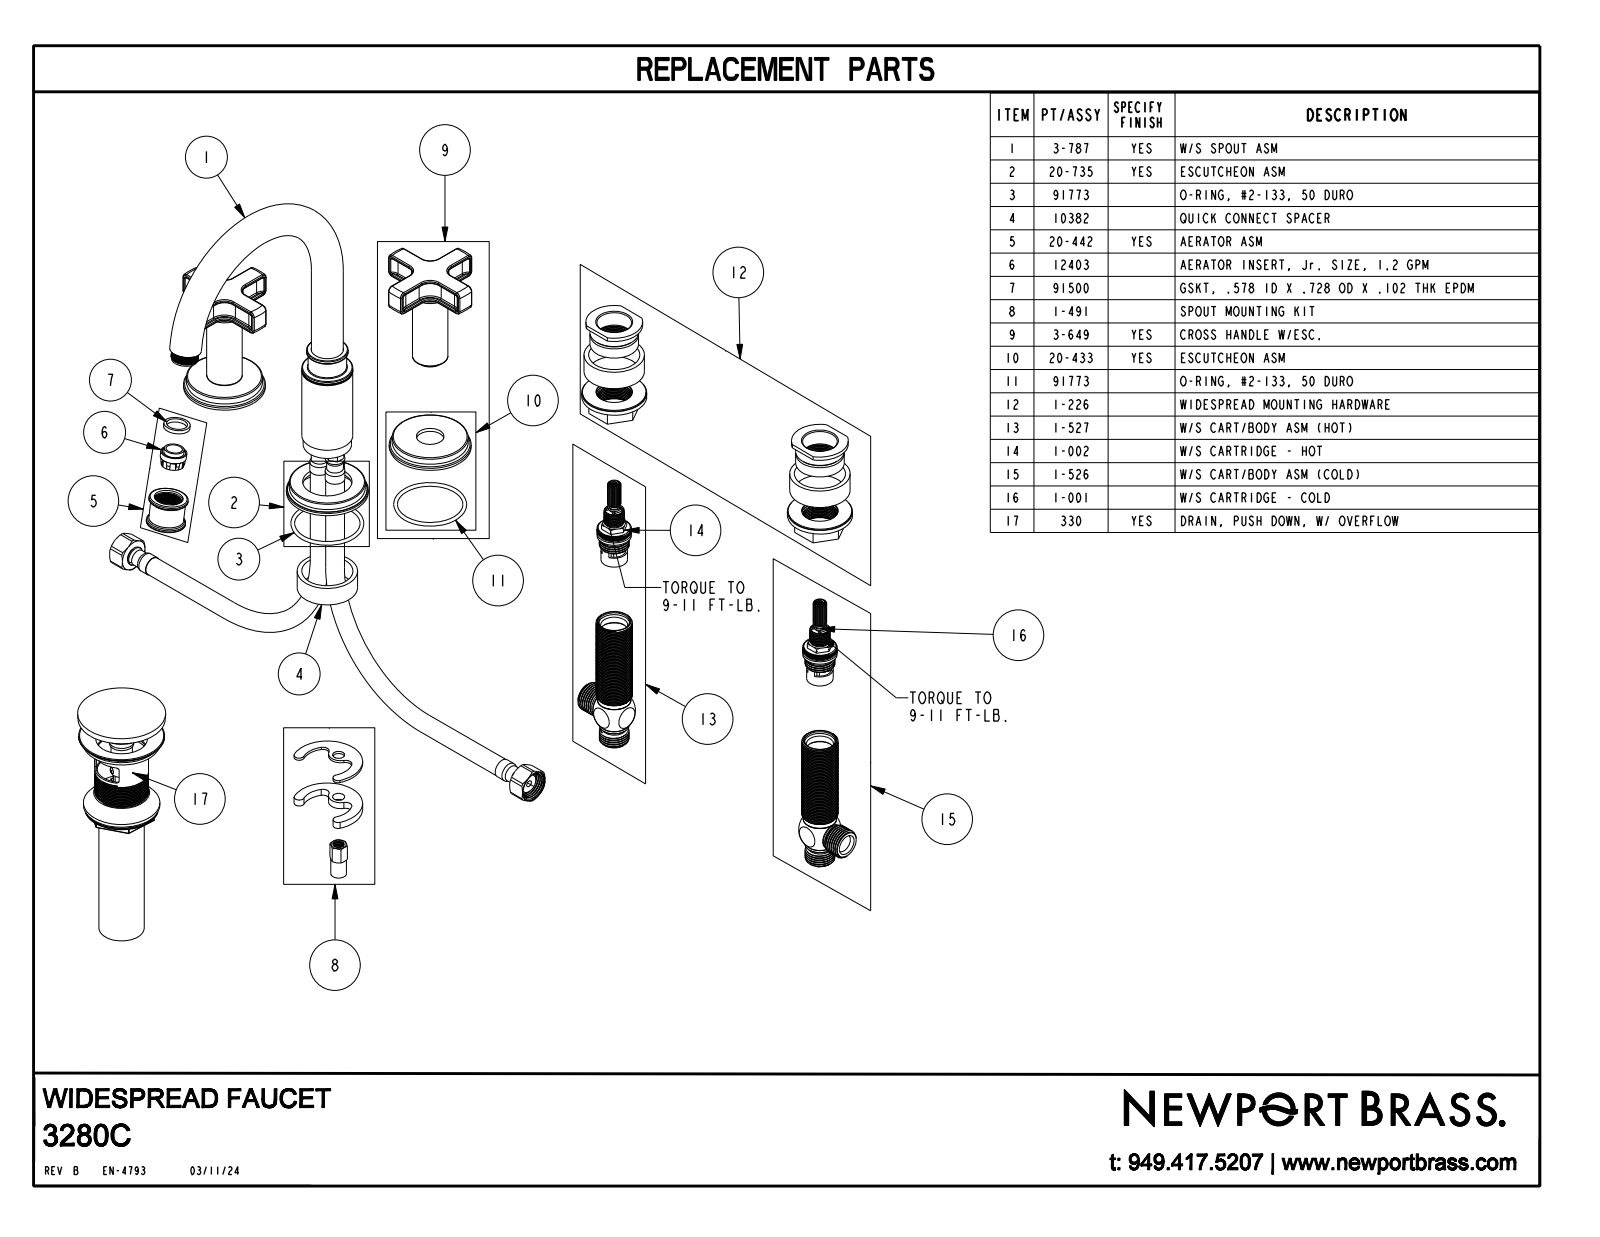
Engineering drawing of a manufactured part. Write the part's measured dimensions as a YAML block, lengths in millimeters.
part_name: "3280C"
step_written_by: "CREO PARAMETRIC BY PTC INC, 2023134 (CONFIG_CONTROL_DESIGN)"
units: millimeters
bodies: {solids: 5, faces: 748, planar: 174, cylindrical: 316, other: 258}
overall_size: [274.3, 231.2, 192]
volume: 347700
surface_area: 77870
round_holes:
  - {diameter: 2.8, count: 2}
  - {diameter: 9.1, count: 2}
  - {diameter: 10.2, count: 2}
  - {diameter: 14.2, count: 2}
  - {diameter: 17.6, count: 1}
round_bosses_or_shafts:
  - {diameter: 57.2, count: 3}
  - {diameter: 53.1, count: 3}
  - {diameter: 24.8, count: 2}
  - {diameter: 22.2, count: 2}
  - {diameter: 21.6, count: 2}
  - {diameter: 35.6, count: 1}
  - {diameter: 29, count: 1}
  - {diameter: 27.4, count: 1}
partial_cylinders:
  - {radius: 0.8, count: 68}
  - {radius: 6.4, count: 16}
  - {radius: 8.3, count: 8}
  - {radius: 10.8, count: 8}
  - {radius: 3.5, count: 2}
  - {radius: 7.9, count: 2}
  - {radius: 35.6, count: 2}
  - {radius: 8.6, count: 1}
face_to_face_distances: [8.9, 82.6, 73.7, 64.8, 55.9, 17.8, 2.5, 7.6, 15.2, 64]
hole_center_spacings: [203.2]
